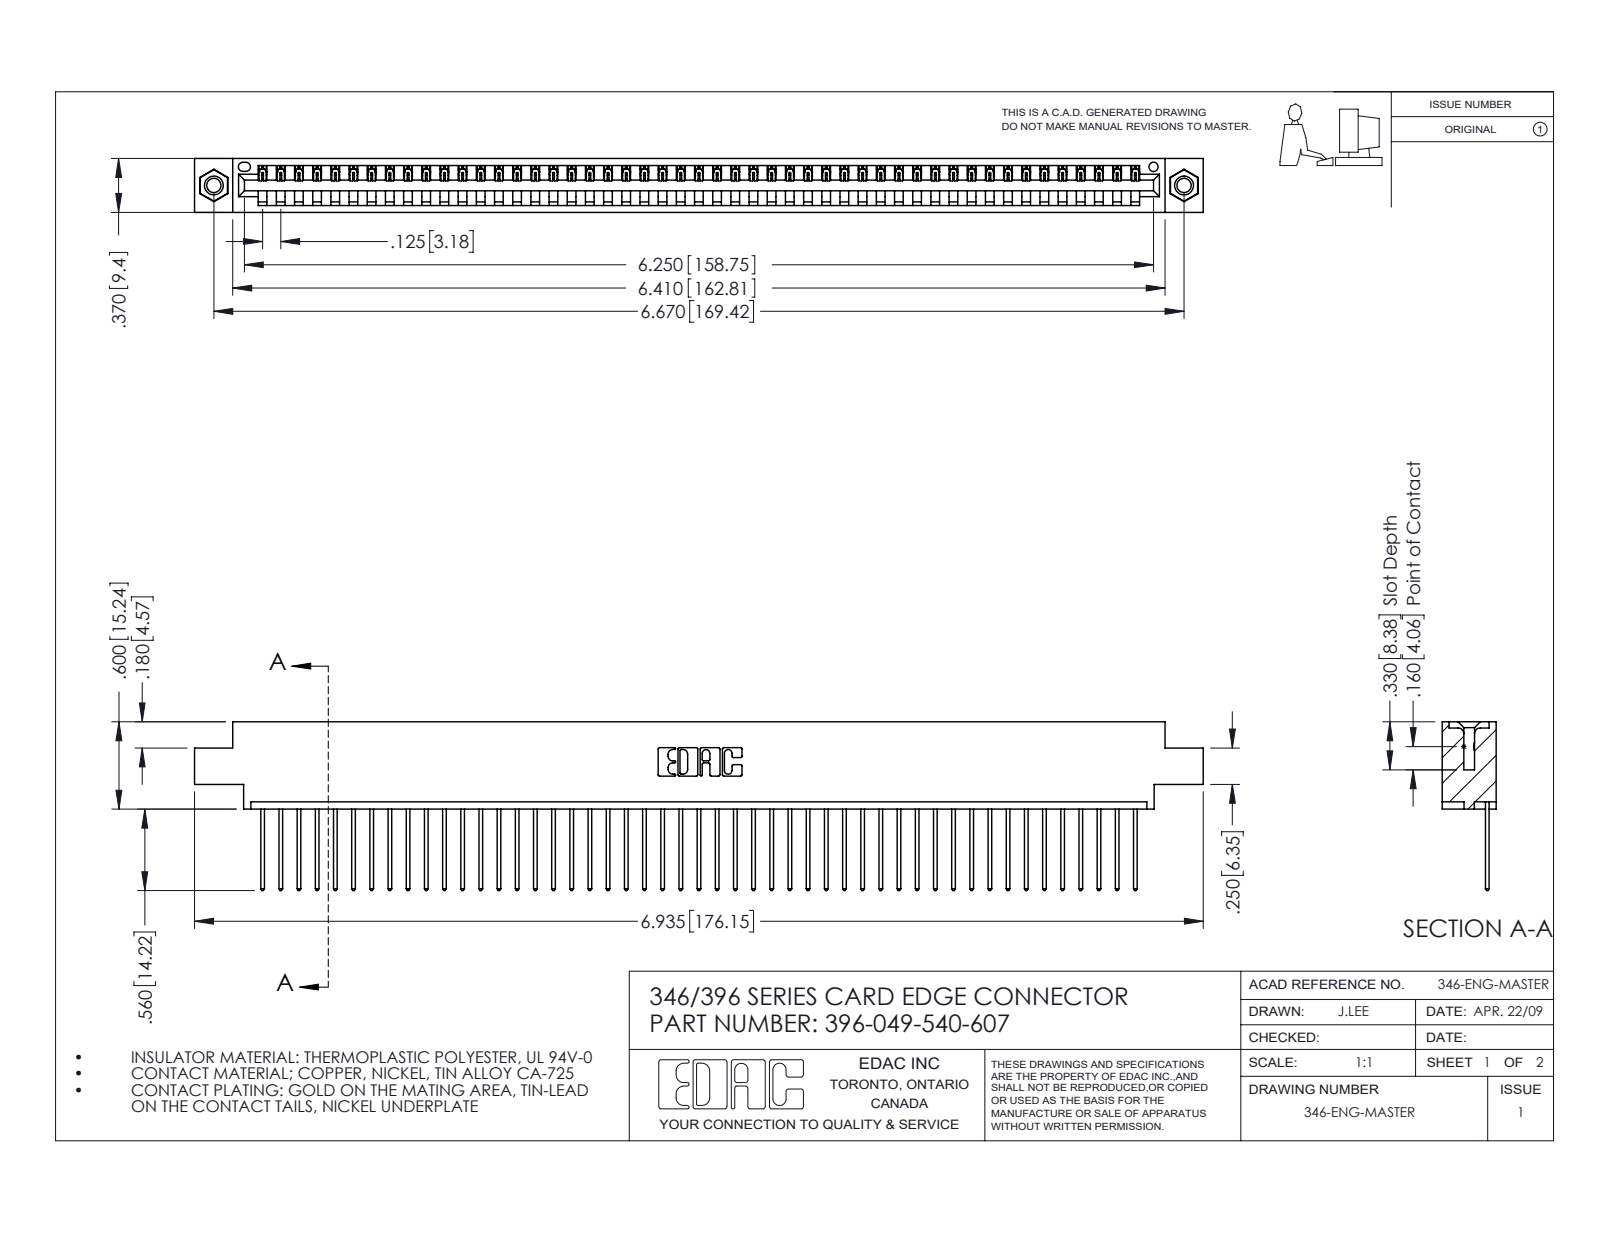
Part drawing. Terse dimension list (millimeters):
name: 345-250-001_345-250-005-103; 346 Part_0.170 Offset - 0.156 Dia-TI; 396-049-540-607; 345-292-001_345-293-140
written by: SolidWorks 2016 (CONFIG_CONTROL_DESIGN)
unit: mm
bodies: 52 solids, 3028 faces (2072 planar, 940 cylindrical, 16 other)
size: 176.1 × 29.5 × 9.4
volume: 16 810 mm³; area: 21 760 mm²
holes: 2× ⌀2.5, 2× ⌀3.2, 2× ⌀4, 1× ⌀1.6
bosses: 2× ⌀3.9
rounds: 98× R0.2, 98× R0.3, 22× R0.3, 6× R0.2, 6× R0.8, 3× R0.7, 2× R0.8, 2× R1
face distances: 1.2, 8.2, 9.4, 6.4, 1.8, 7.6, 0.6, 5.6, 3.8, 2.5
hole spacings: 6.2, 164.1, 169.4
